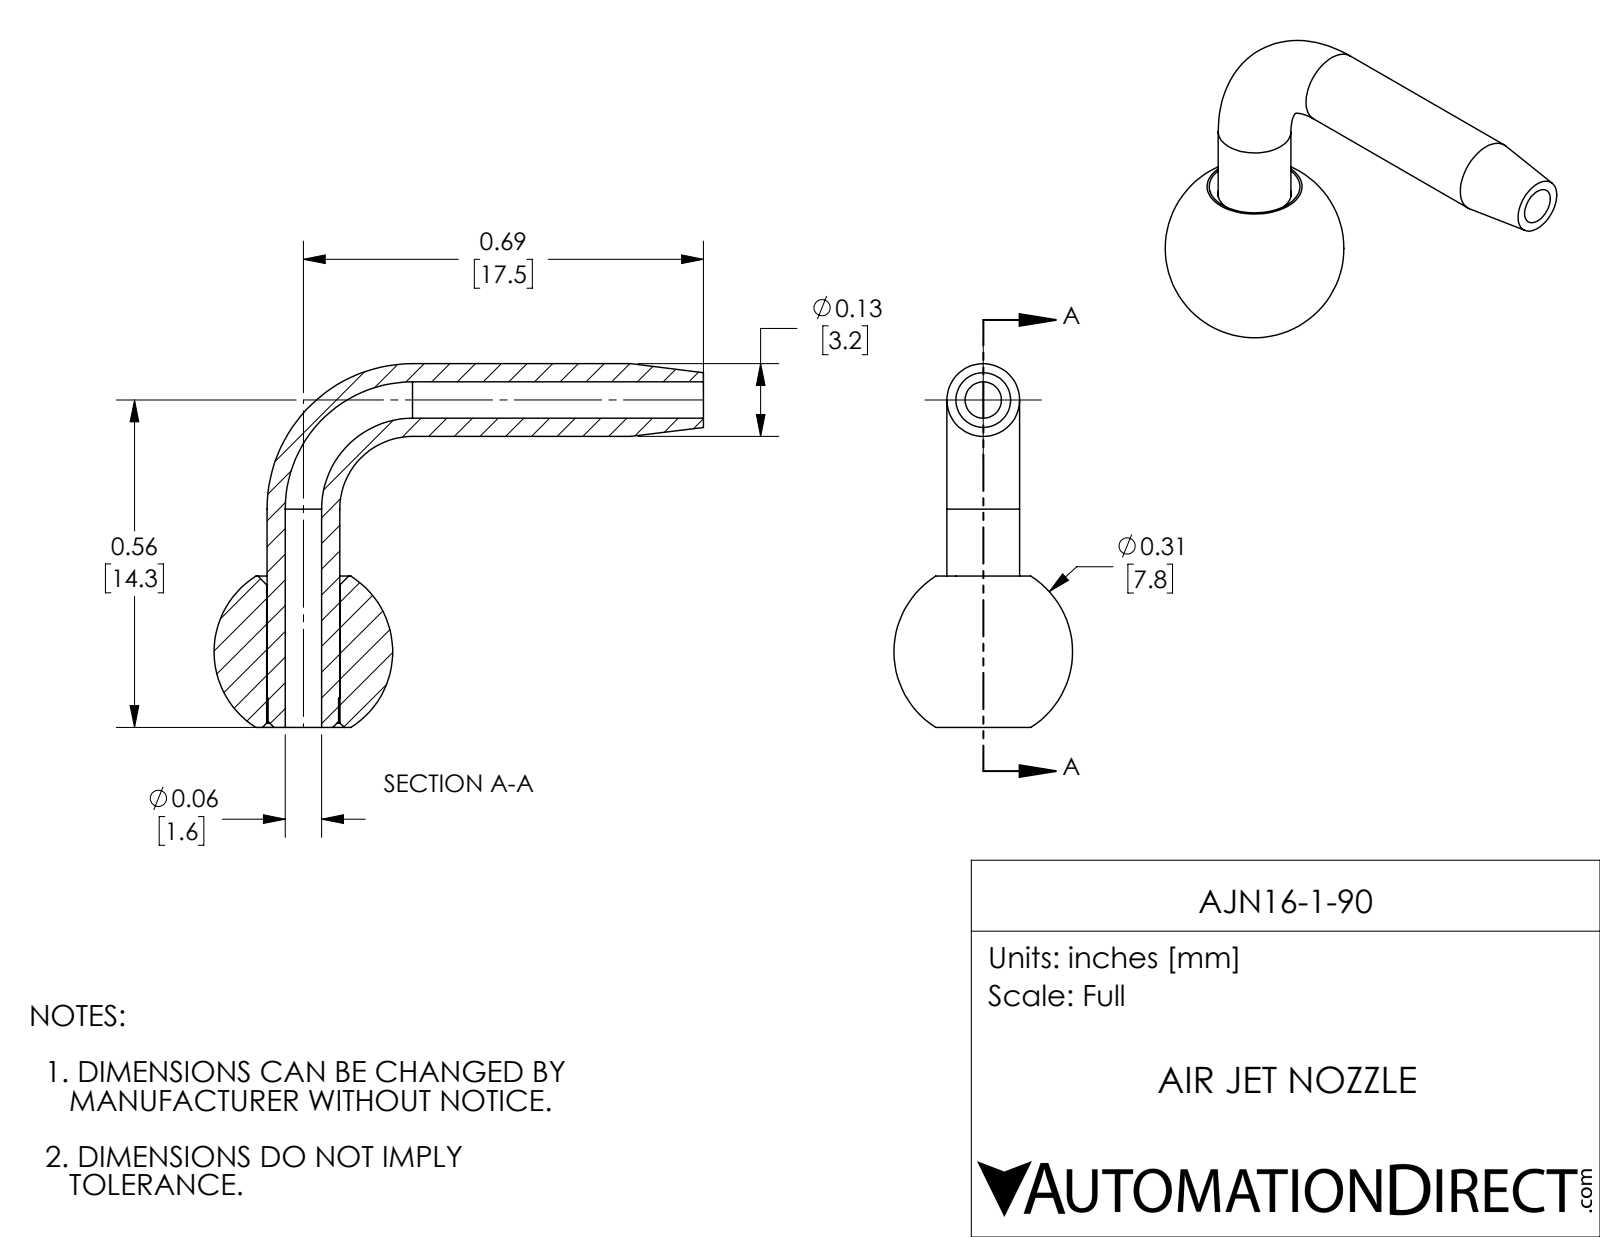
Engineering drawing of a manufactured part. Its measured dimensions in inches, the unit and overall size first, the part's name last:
Units: inches
Overall size (bounding box): 0.841 × 0.625 × 0.307
Round holes (diameter × count): ⌀0.063 ×2, ⌀0.126 ×1
Round bosses / shafts (diameter × count): ⌀0.125 ×2, ⌀0.121 ×1
Main face-to-face distances: 0.26, 0.05, 0.21
Volume: 0.022 in³ · Surface area: 1.059 in²
Bodies: 2 solids, 31 faces (5 planar, 12 cylindrical, 14 other)
Part name (STEP PRODUCT): AJN16-1-90
STEP written by: SolidWorks 2018 (AUTOMOTIVE_DESIGN)
